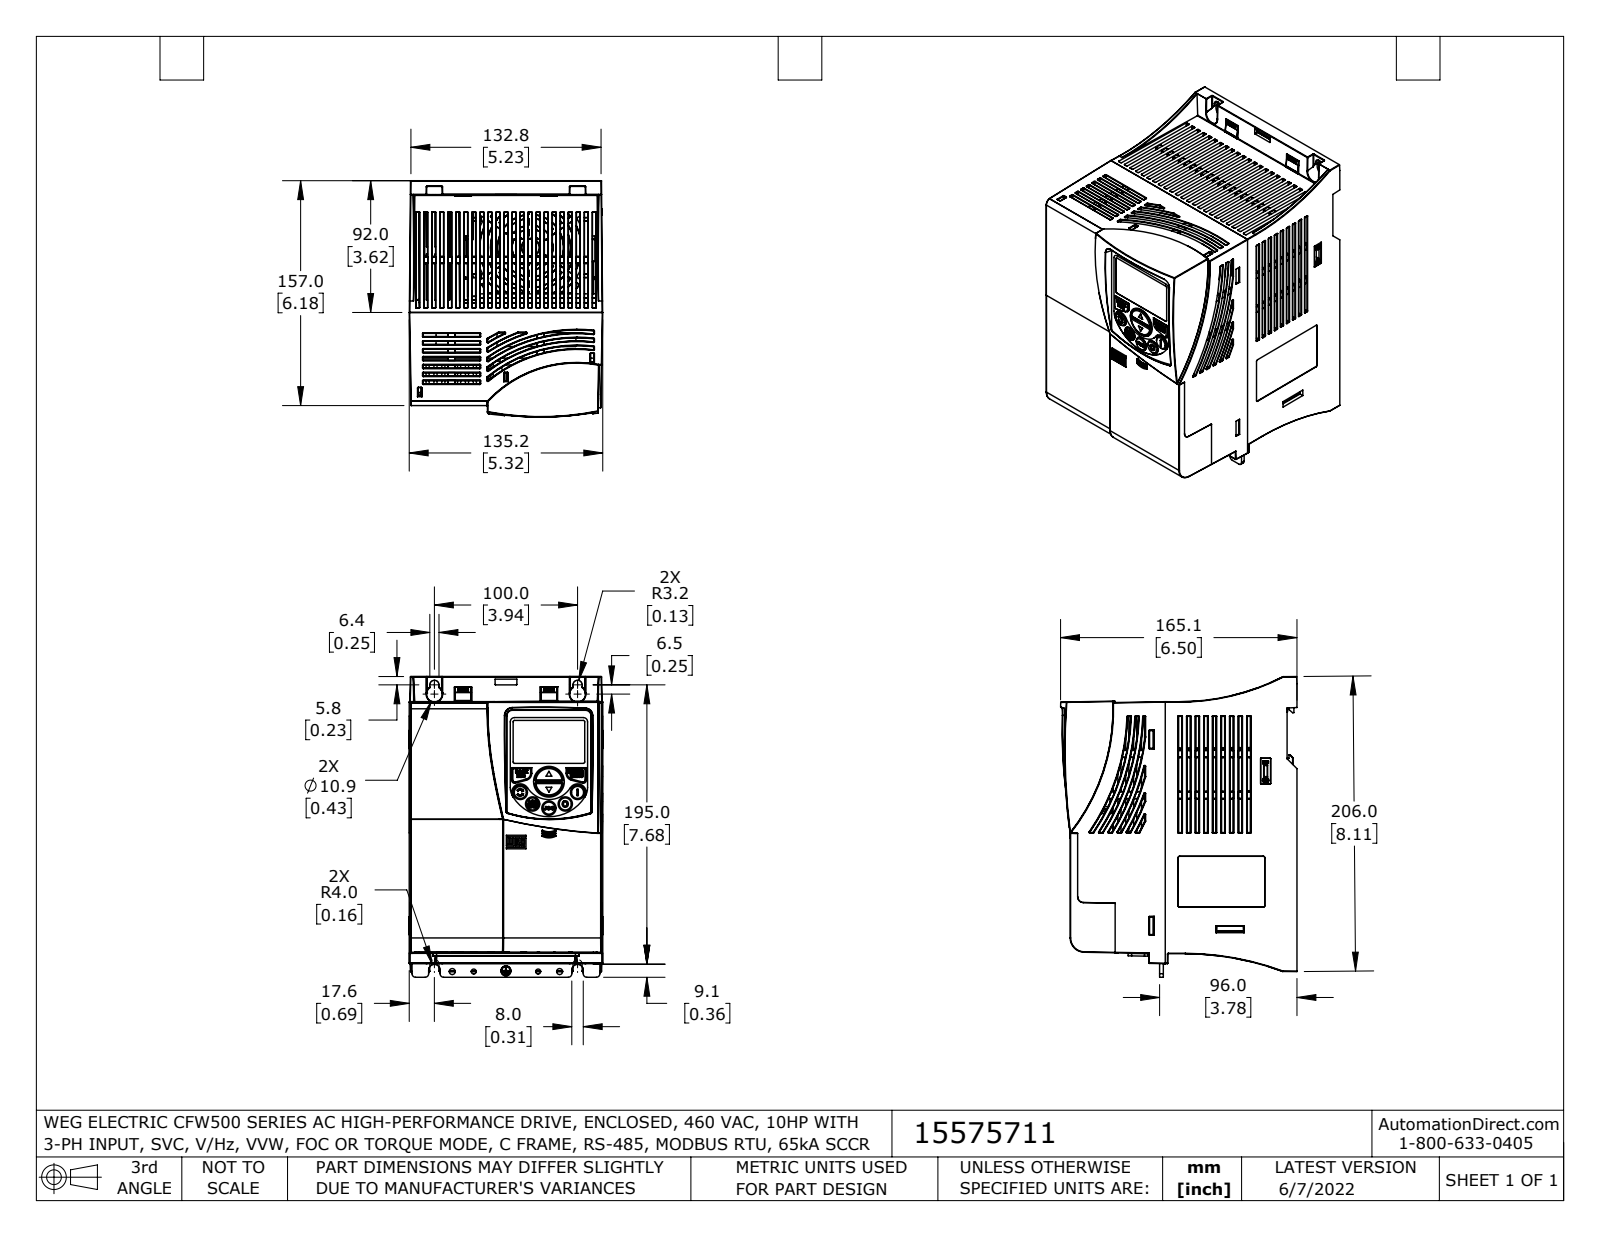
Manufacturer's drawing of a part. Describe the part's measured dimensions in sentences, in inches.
The part is named "CFW500 MEC C IP20 nc coord fxt r1B New2 fxt". Its 3-D file was written by "SolidWorks 2021 (AUTOMOTIVE_DESIGN)". It is 1 solid with 3702 faces: 1564 planar, 810 cylindrical and 1328 other. Overall it measures 8.266 by 6.501 by 5.322 inches. Its volume is 209.8 cubic inches and its surface area 362.5 square inches. Round holes: 3 of diameter 0.394, 2 of diameter 0.138, 2 of diameter 0.165, 2 of diameter 0.386, 1 of diameter 0.152, 1 of diameter 0.787, 1 of diameter 0.846. Round bosses or shafts: 2 of diameter 0.394, 1 of diameter 0.173. Partial cylindrical surfaces (rounded edges, fillets, slot ends): 297 of radius 0.012, 150 of radius 0.008, 39 of radius 0.02, 19 of radius 0.039, 10 of radius 0.098, 4 of radius 0.157, 3 of radius 0.382, 3 of radius 0.413. The main face-to-face distances are 5.76, 0.122, 0.056, 0.059, 5.843, 5.787, 5.906, 0.146, 0.048, 5.808. The hole center spacings are 0.464, 0.898, 0.591, 0.759, 0.841, 1.277, 2.362, 5.226.
